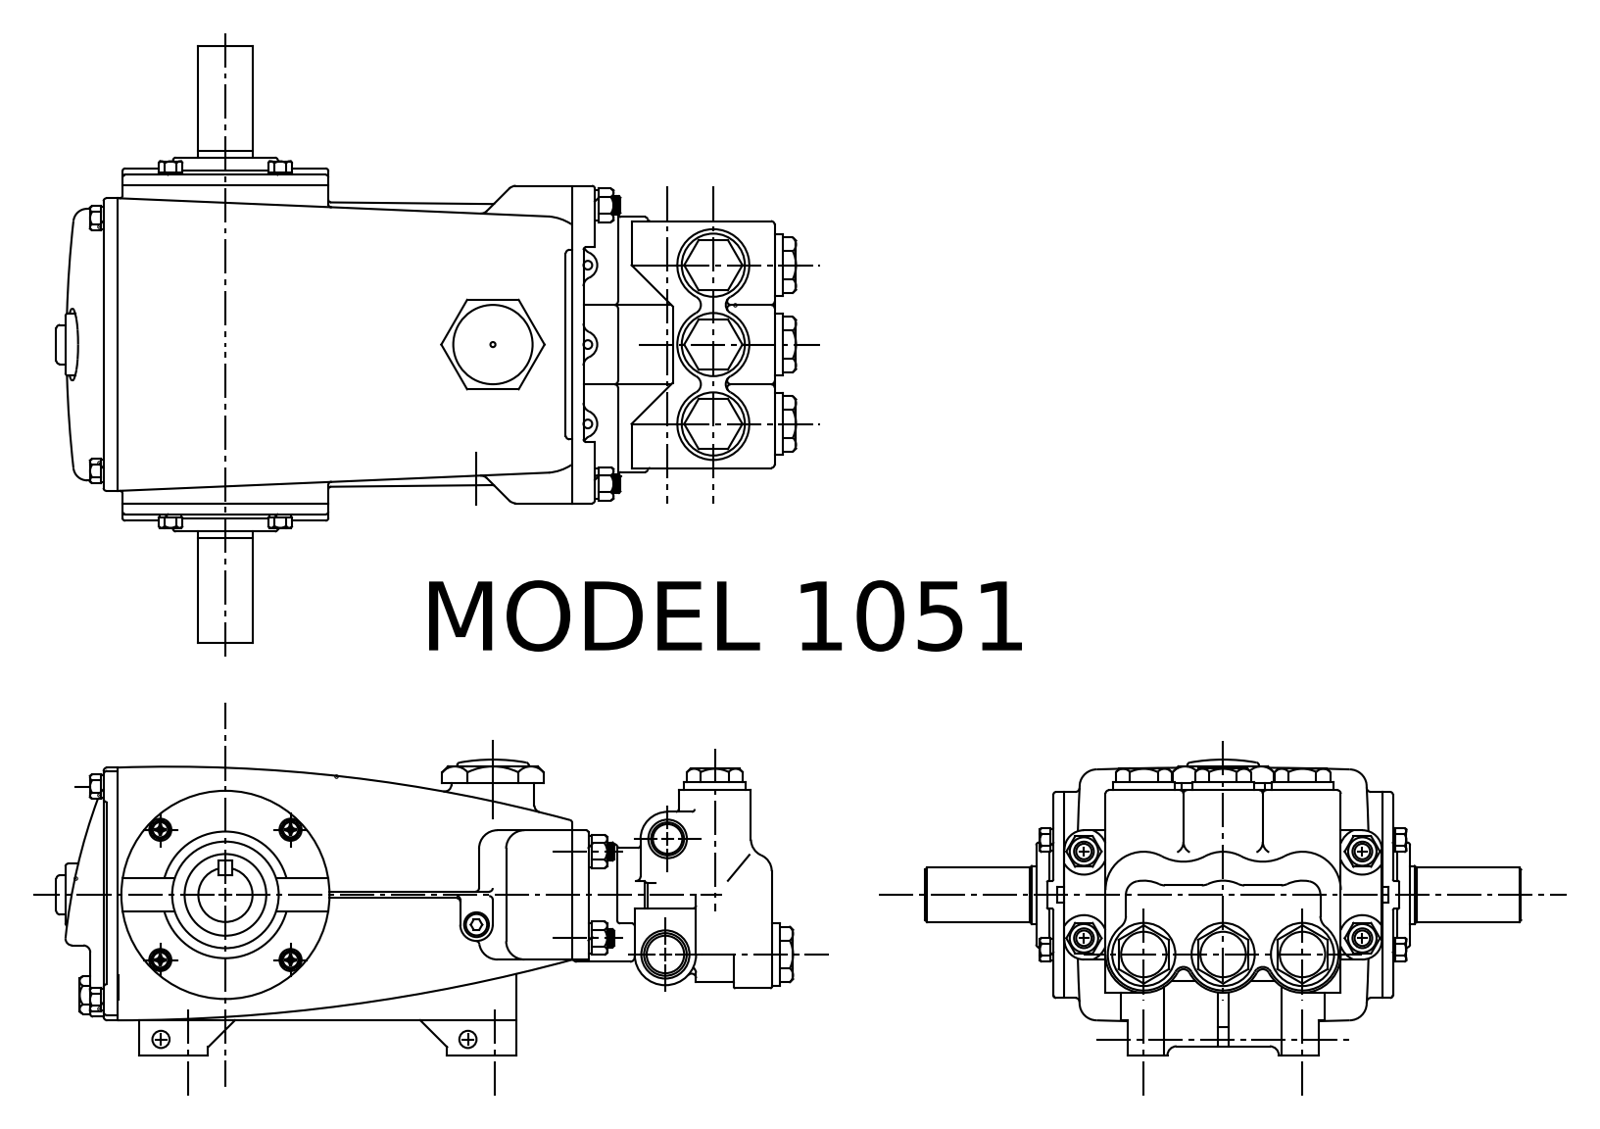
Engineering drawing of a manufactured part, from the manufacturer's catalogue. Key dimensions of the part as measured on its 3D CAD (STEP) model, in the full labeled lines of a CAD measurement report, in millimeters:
Part name (STEP PRODUCT): Hex Nut Style 1_AM_B18.2.4.1M - Hex nut, Style 1, M10 x 1.5, with 16mm WAF --D-N; 14050; 46704; 15frame_drive_end (+1 more)
STEP written by: SolidWorks 2009 (AUTOMOTIVE_DESIGN)
Units: millimetres
Bodies: 10 solids, 1125 faces (535 planar, 337 cylindrical, 253 other)
Overall size (bounding box): 413.4 × 329.9 × 164.9
Volume: 7 527 000 mm³ · Surface area: 388 100 mm²
Round holes (diameter × count): ⌀8.5 ×8, ⌀11 ×6, ⌀20.3 ×6, ⌀10 ×4, ⌀45.7 ×2, ⌀17.9 ×1, ⌀23 ×1, ⌀38.1 ×1
Round bosses / shafts (diameter × count): ⌀11.2 ×8, ⌀10.7 ×8, ⌀34.4 ×4, ⌀43.2 ×2, ⌀34.4 ×2, ⌀5.1 ×2, ⌀115.1 ×1, ⌀114.3 ×1
Partial cylindrical surfaces — rounded edges, fillets, slot ends (radius × count): R5.1 ×25, R2.5 ×15, R1.3 ×14, R3.8 ×5, R7.6 ×5, R4.1 ×4, R4.6 ×4, R21.6 ×4
Main face-to-face distances: 12.7, 30.7, 162.8, 22.9, 32.7, 122.3, 17.5, 4.8, 193.5, 96.5
Hole centre spacings: 48.3, 44.5, 80.5, 72, 36.1, 39.4, 39.4, 59.9
